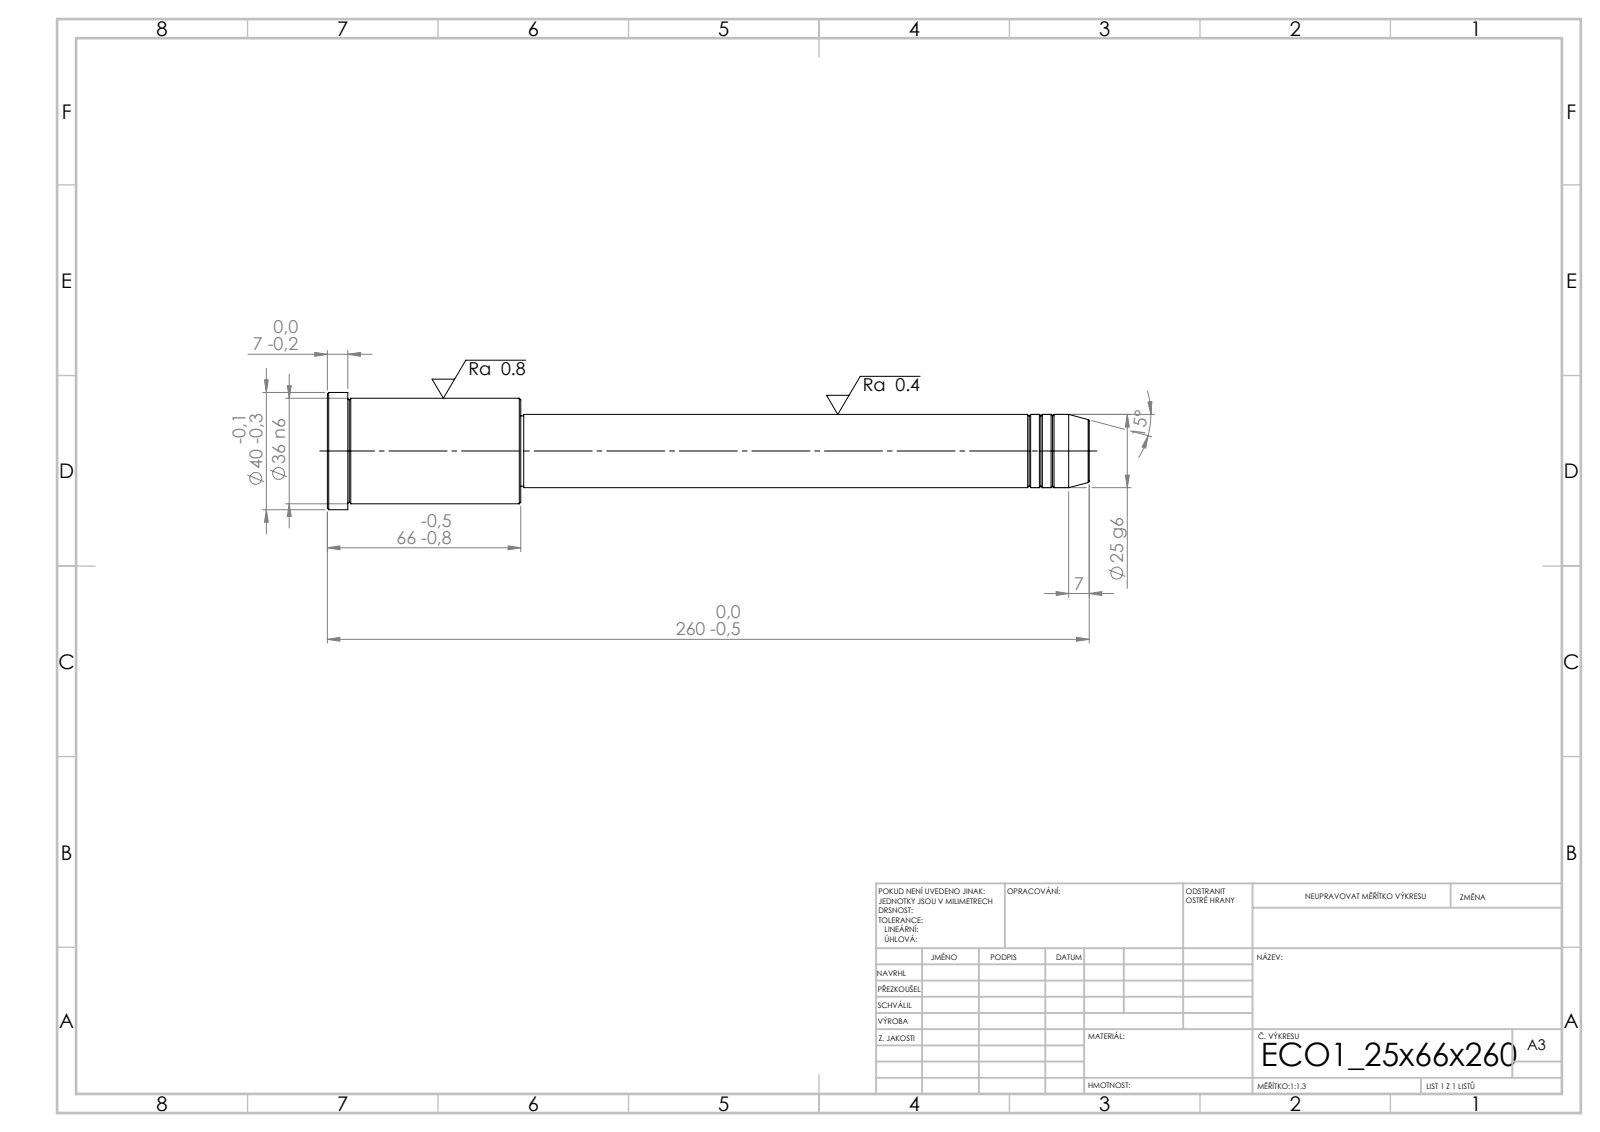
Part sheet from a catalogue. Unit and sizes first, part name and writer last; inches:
Units: inches
Overall size (bounding box): 10.236 × 1.575 × 1.575
Round bosses / shafts (diameter × count): ⌀1.575 ×1, ⌀1.417 ×1, ⌀0.984 ×1, ⌀0.945 ×1
Main face-to-face distances: 2.598, 7.638, 10.236, 9.961, 2.323, 0.276, 7.598, 0.039, 2.362, 2.638
Volume: 9.97 in³ · Surface area: 39.25 in²
Bodies: 1 solid, 43 faces (5 planar, 14 cylindrical, 24 other)
STEP written by: SolidWorks 2019 (CONFIG_CONTROL_DESIGN)
